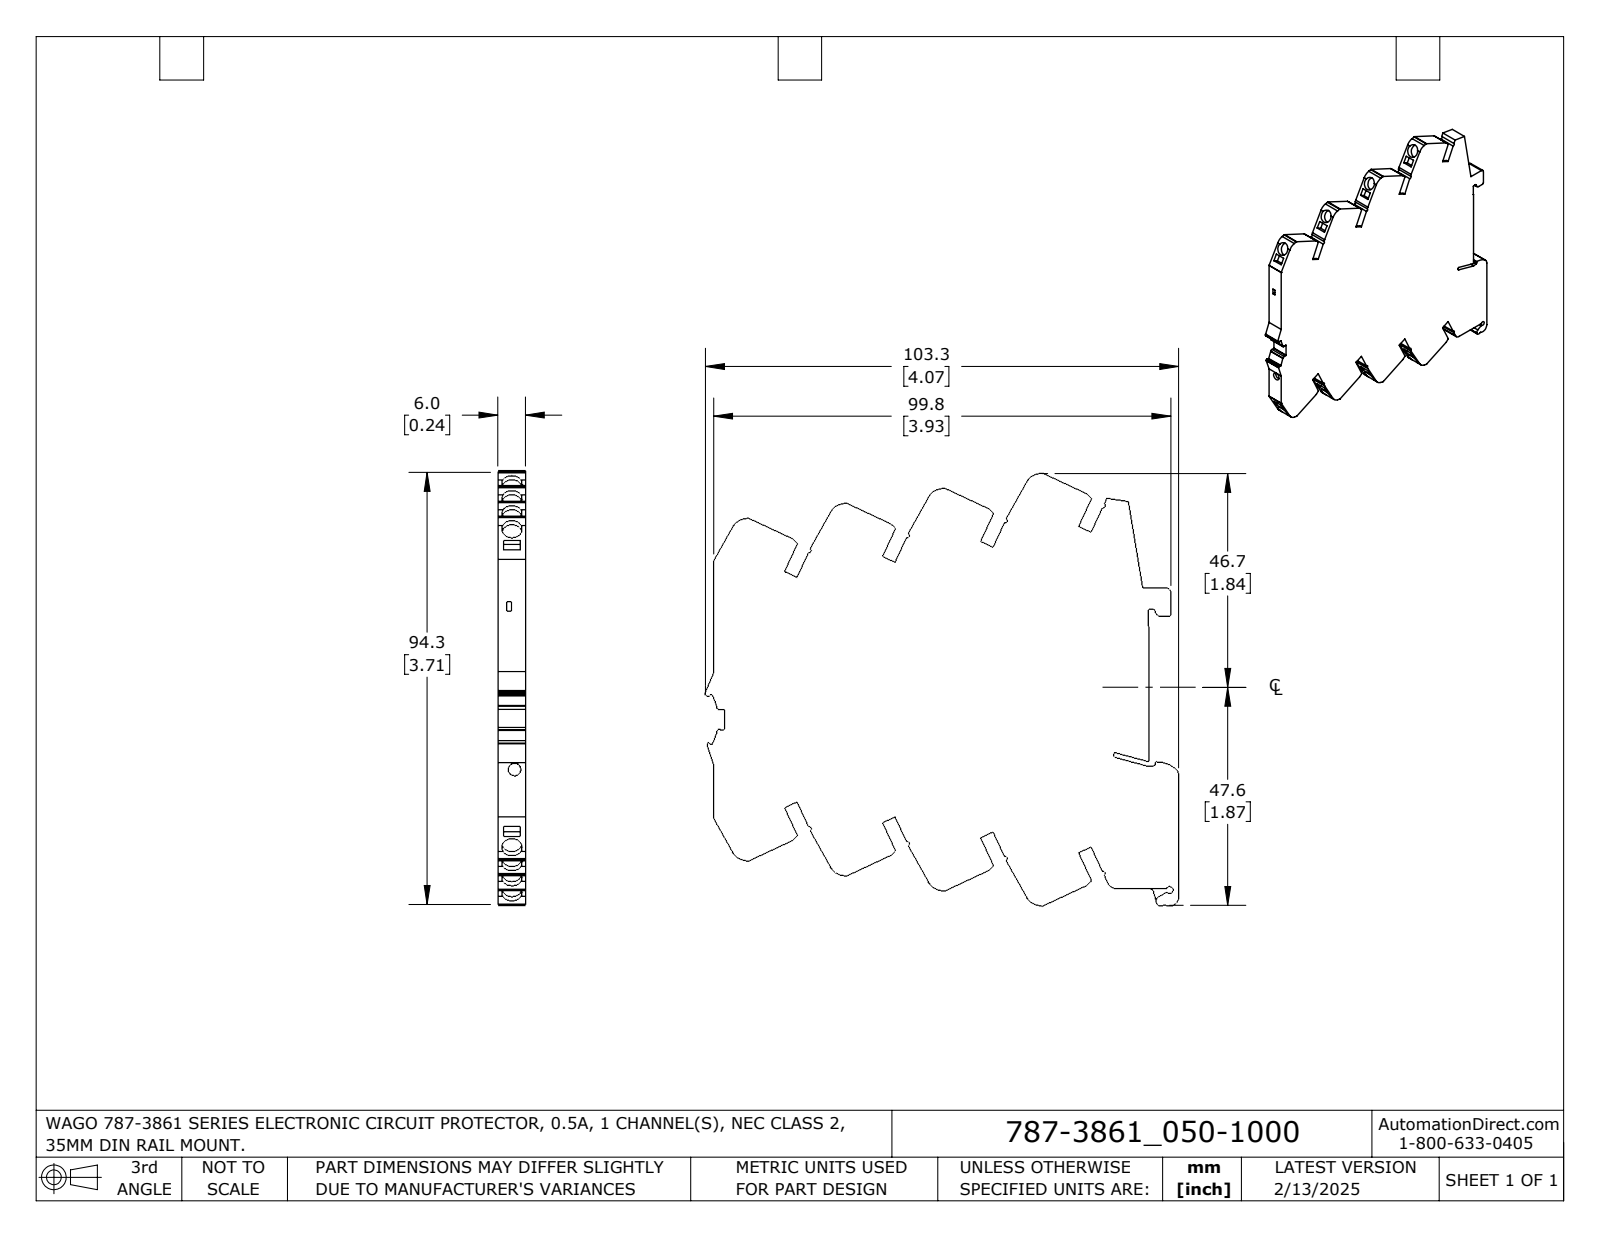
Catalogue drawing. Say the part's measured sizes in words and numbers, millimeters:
The part is named "787-3861_050-1000_HI". Its 3-D file was written by "SolidWorks 2024 (AUTOMOTIVE_DESIGN)". It is 1 solid with 262 faces: 197 planar, 65 cylindrical and 0 other. Overall it measures 103.3 by 94.26 by 6 millimeters. Its volume is 43 992 cubic millimeters and its surface area 18 864 square millimeters. Round holes: 8 of diameter 4.4, 1 of diameter 2.7. Partial cylindrical surfaces (rounded edges, fillets, slot ends): 13 of radius 0.2, 12 of radius 0.5, 8 of radius 0.4, 8 of radius 3.35, 5 of radius 1, 3 of radius 0.3, 3 of radius 2, 2 of radius 0.45. The main face-to-face distances are 6, 17.99, 17.02, 12.01, 3, 35.98, 12, 24.01, 14.99, 34.04. The hole center spacings are 13.35, 13.34, 26.7, 26.71, 40.05.
